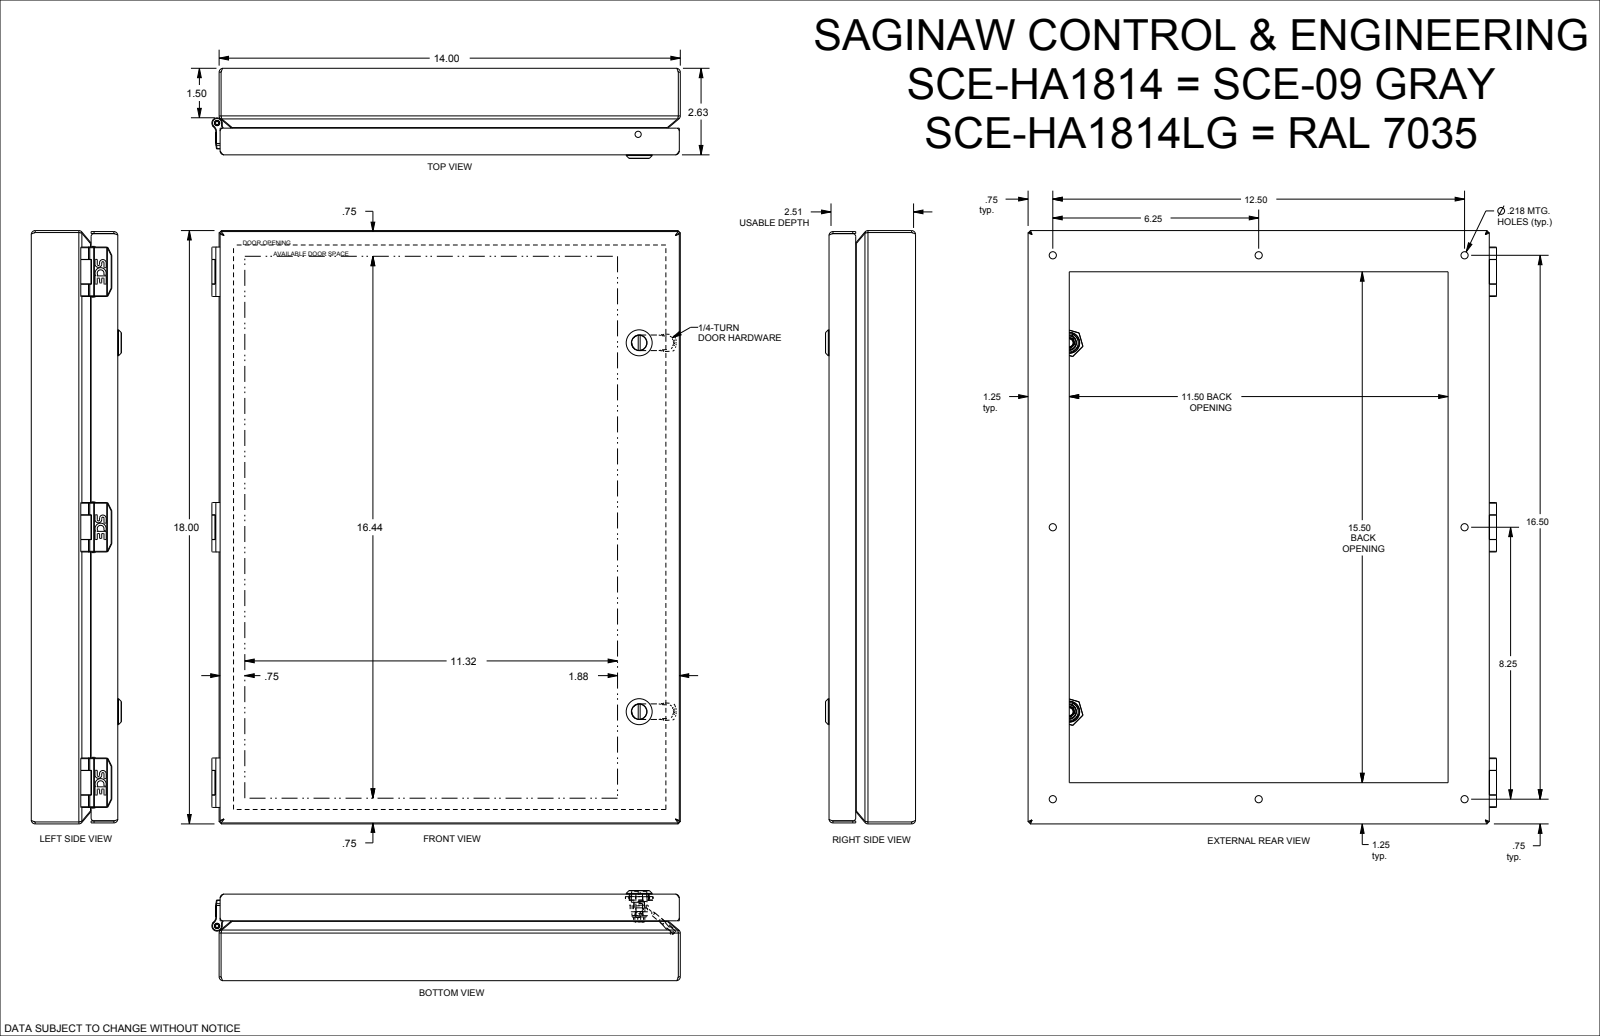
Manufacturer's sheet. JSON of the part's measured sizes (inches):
{"part_name": "SCE-HA1814", "step_written_by": "SolidWorks 2021 (AUTOMOTIVE_DESIGN)", "units": "inches", "bodies": {"solids": 33, "faces": 2284, "planar": 910, "cylindrical": 594, "other": 780}, "overall_size": [18.06, 14.22, 2.733], "volume_in3": 36.67, "surface_area_in2": 1161, "round_holes": [[0.218, 8], [0.164, 3], [0.17, 3], [0.174, 3], [0.338, 3], [0.2, 2], [0.239, 2], [0.254, 2], [0.269, 2], [0.282, 2], [0.326, 2], [0.475, 2]], "round_bosses_or_shafts": [[0.479, 3], [0.26, 3], [0.15, 3], [0.788, 2], [0.548, 2], [0.46, 2], [0.43, 2], [0.35, 2]], "partial_cylinders_radius": [[0.106, 99], [0.005, 54], [0.008, 48], [0.02, 32], [0.025, 18], [0.01, 16], [0.05, 16], [0.06, 12]], "face_to_face_distances": [0.06, 0.059, 2.566, 2.626, 2.507, 2.567, 14.001, 0.031, 0.09, 18.001], "hole_center_spacings": [6.276, 7.75, 8.276, 10.387, 15.035, 17.702, 12.552, 16.552]}
